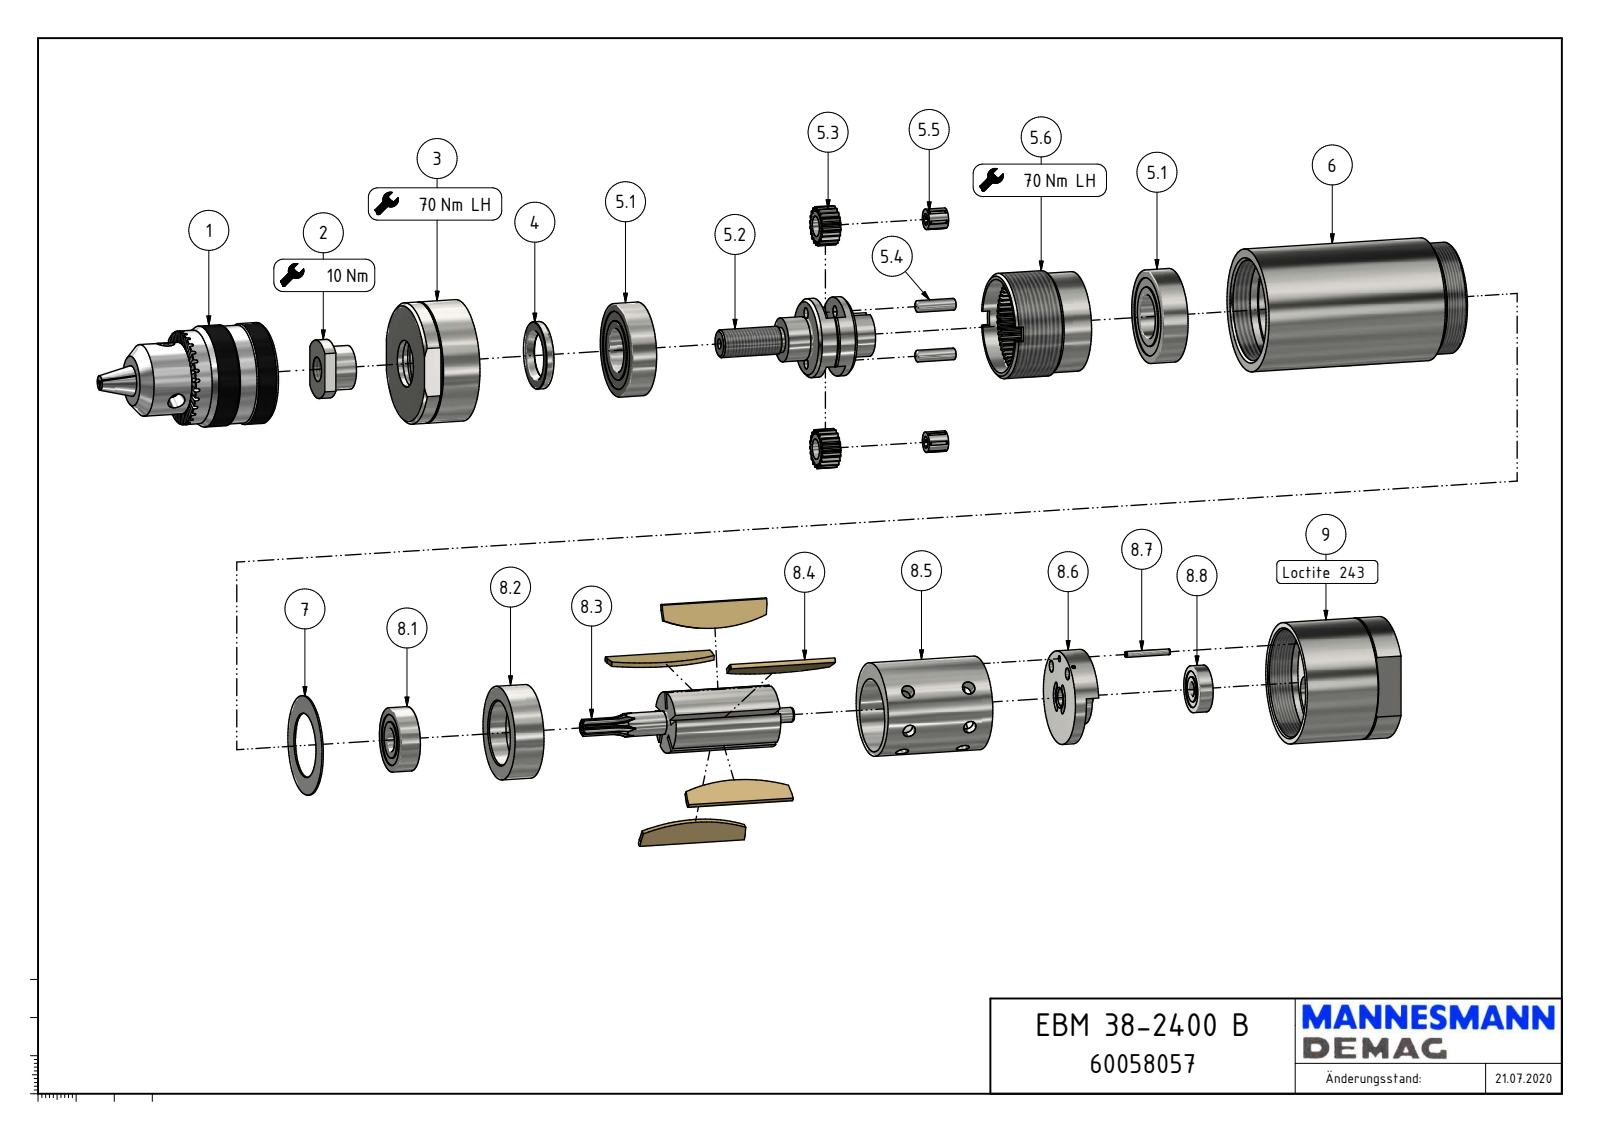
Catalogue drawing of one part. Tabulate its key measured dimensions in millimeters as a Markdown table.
| quantity | value |
| --- | --- |
| part name | EBM 38-2400 B_60058057 |
| STEP written by | Autodesk Inventor 2016 (AUTOMOTIVE_DESIGN) |
| units | millimeters |
| bodies | 1 solid, 363 faces (235 planar, 59 cylindrical, 69 other) |
| overall size | 186 × 42 × 42 |
| volume | 195 062 mm³ |
| surface area | 28 897 mm² |
| round holes (diameter × count) | 6 × 3, 11.45 × 3, 1.5 × 1, 1.6 × 1, 4 × 1, 8.38 × 1, 9.75 × 1, 16 × 1, 18.2 × 1, 23 × 1 |
| round bosses / shafts (diameter × count) | 42 × 1, 41.5 × 1, 36 × 1, 34.5 × 1, 33.5 × 1, 32 × 1, 24.5 × 1, 14.95 × 1 |
| partial cylindrical surfaces (radius × count) | 0.5 × 30, 10 × 1 |
| main face-to-face distances | 120, 127, 7, 21, 37, 106.75, 28, 99, 1, 26.5 |
| hole center spacings | 11.72, 20.12, 10.5, 18 |
